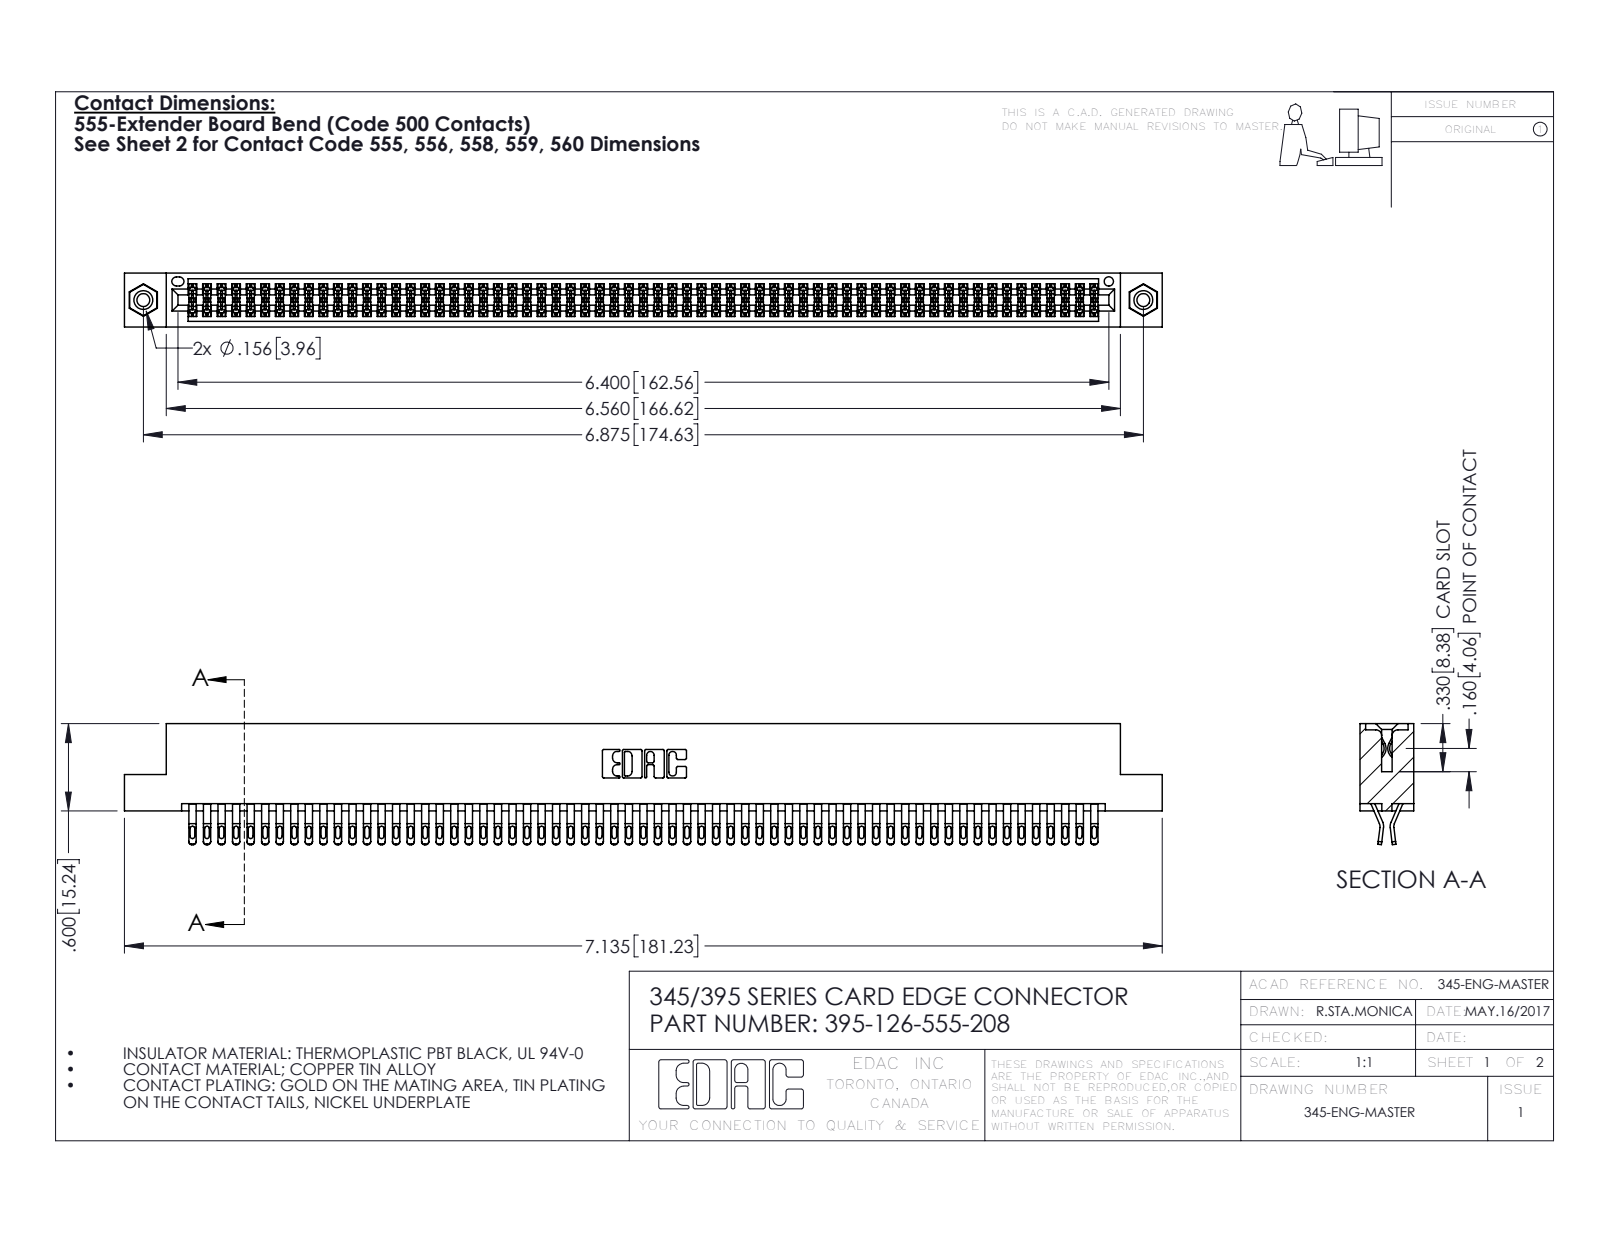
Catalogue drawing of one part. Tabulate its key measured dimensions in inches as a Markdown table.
| quantity | value |
| --- | --- |
| part name | 345 Part_Flush Mounting Lugs - 0.156 Dia-TI; 395-126-555-208; 345-250-001_345-250-003-102; 345-292-001_555 Tail |
| STEP written by | SolidWorks 2016 (CONFIG_CONTROL_DESIGN) |
| units | inches |
| bodies | 129 solids, 7242 faces (4018 planar, 3208 cylindrical, 16 other) |
| overall size | 7.135 × 0.832 × 0.37 |
| volume | 1.108 in³ |
| surface area | 44.23 in² |
| round holes (diameter × count) | 0.089 × 2, 0.125 × 2, 0.156 × 2, 0.064 × 1 |
| round bosses / shafts (diameter × count) | 0.155 × 2 |
| partial cylindrical surfaces (radius × count) | 0.016 × 315, 0.02 × 252, 0.006 × 189, 0.01 × 22, 0.007 × 6, 0.031 × 6, 0.026 × 3, 0.01 × 2 |
| main face-to-face distances | 0.072, 0.298, 0.025, 0.37, 0.2, 0.098, 0.272, 0.225, 0.175, 0.149 |
| hole center spacings | 0.27, 6.639, 6.875 |
